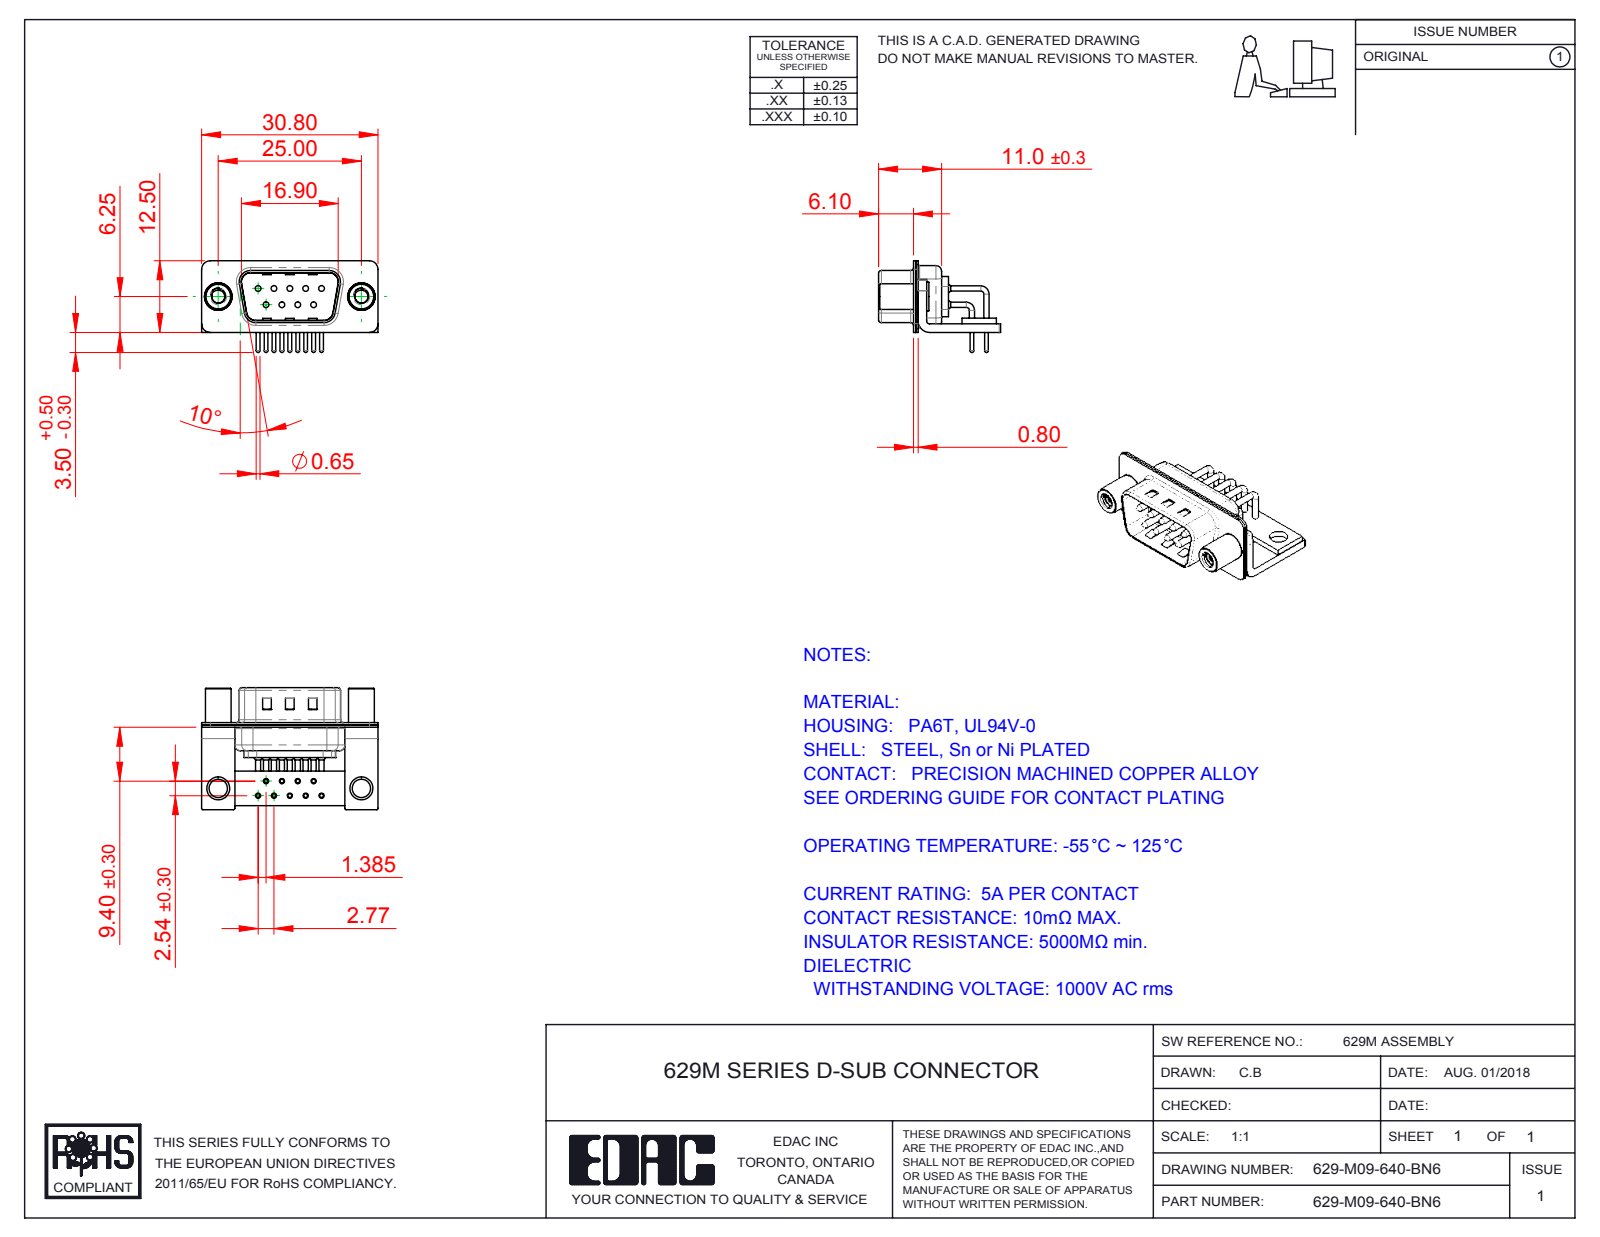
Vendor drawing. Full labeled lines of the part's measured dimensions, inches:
Part name (STEP PRODUCT): 629M 4-40 Threaded Standoff; 629M Stabilizer Bracket; 629M Housing_09 Contacts; 629M Shell Rear_09 Contacts (+5 more)
STEP written by: SolidWorks 2016 (CONFIG_CONTROL_DESIGN)
Units: inches
Bodies: 17 solids, 1412 faces (711 planar, 535 cylindrical, 166 other)
Overall size (bounding box): 1.213 × 0.839 × 0.63
Volume: 0.118 in³ · Surface area: 8.164 in²
Round holes (diameter × count): ⌀0.035 ×9, ⌀0.039 ×9, ⌀0.067 ×9, ⌀0.079 ×9, ⌀0.089 ×2, ⌀0.126 ×2, ⌀0.157 ×2, ⌀0.189 ×2
Round bosses / shafts (diameter × count): ⌀0.059 ×9, ⌀0.035 ×9, ⌀0.026 ×9, ⌀0.197 ×2, ⌀0.193 ×2, ⌀0.177 ×2
Partial cylindrical surfaces — rounded edges, fillets, slot ends (radius × count): R0.01 ×16, R0.059 ×16, R0.079 ×13, R0.02 ×9, R0.04 ×9, R0.063 ×8, R0.024 ×4, R0.026 ×4
Main face-to-face distances: 0.016, 0.059, 0.031, 0.033, 0.049, 0.075, 0.039, 0.098, 0.409, 0.376
Hole centre spacings: 0.109, 0.218, 0.124, 0.192, 0.327, 0.114, 0.114, 0.198
